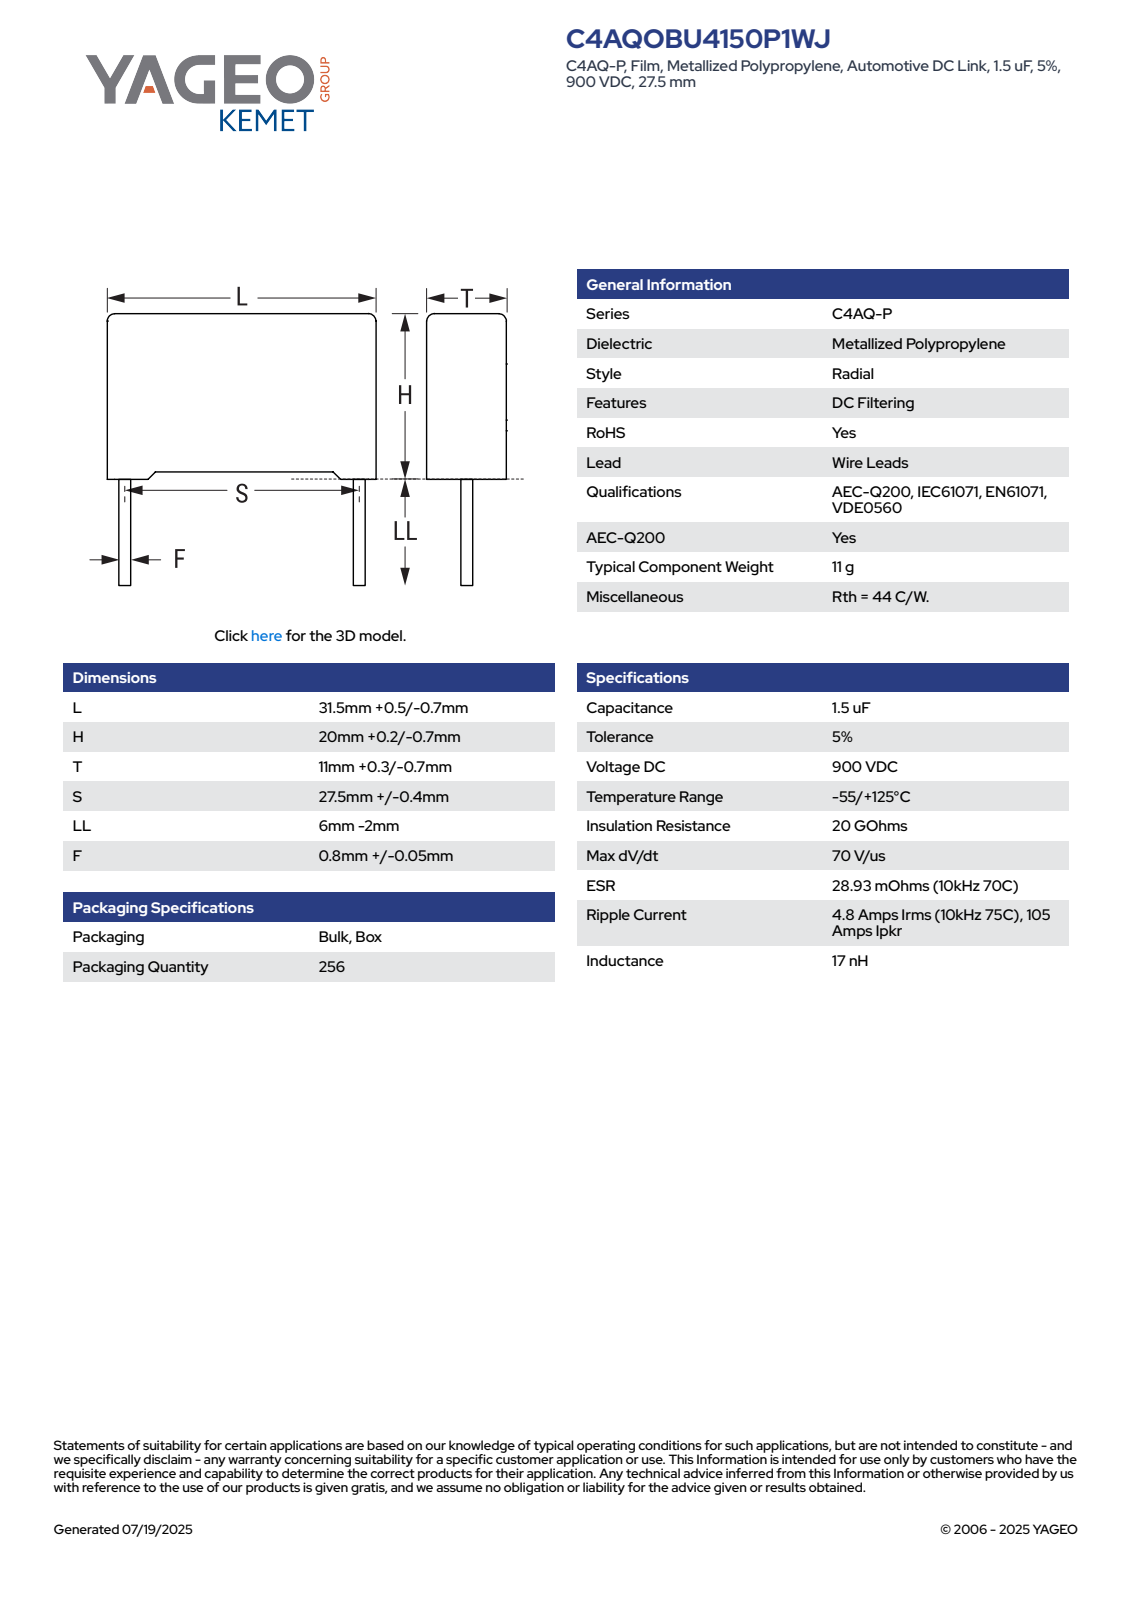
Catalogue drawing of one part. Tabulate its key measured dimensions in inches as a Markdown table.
| quantity | value |
| --- | --- |
| part name | CFR_RB2CFP_31.5X20X11_L32H20.2T11.3S27.5LL4F0.85 |
| STEP written by | SolidWorks 2014 (AUTOMOTIVE_DESIGN) |
| units | inches |
| bodies | 4 solids, 85 faces (77 planar, 8 cylindrical, 0 other) |
| overall size | 1.26 × 0.953 × 0.445 |
| volume | 0.431 in³ |
| surface area | 3.953 in² |
| round bosses / shafts (diameter × count) | 0.033 × 2 |
| partial cylindrical surfaces (radius × count) | 0.02 × 4 |
| main face-to-face distances | 0.445, 0.766, 1.26, 0.768, 0.028, 0.03, 0.795, 0.042, 0.445, 1.218 |
